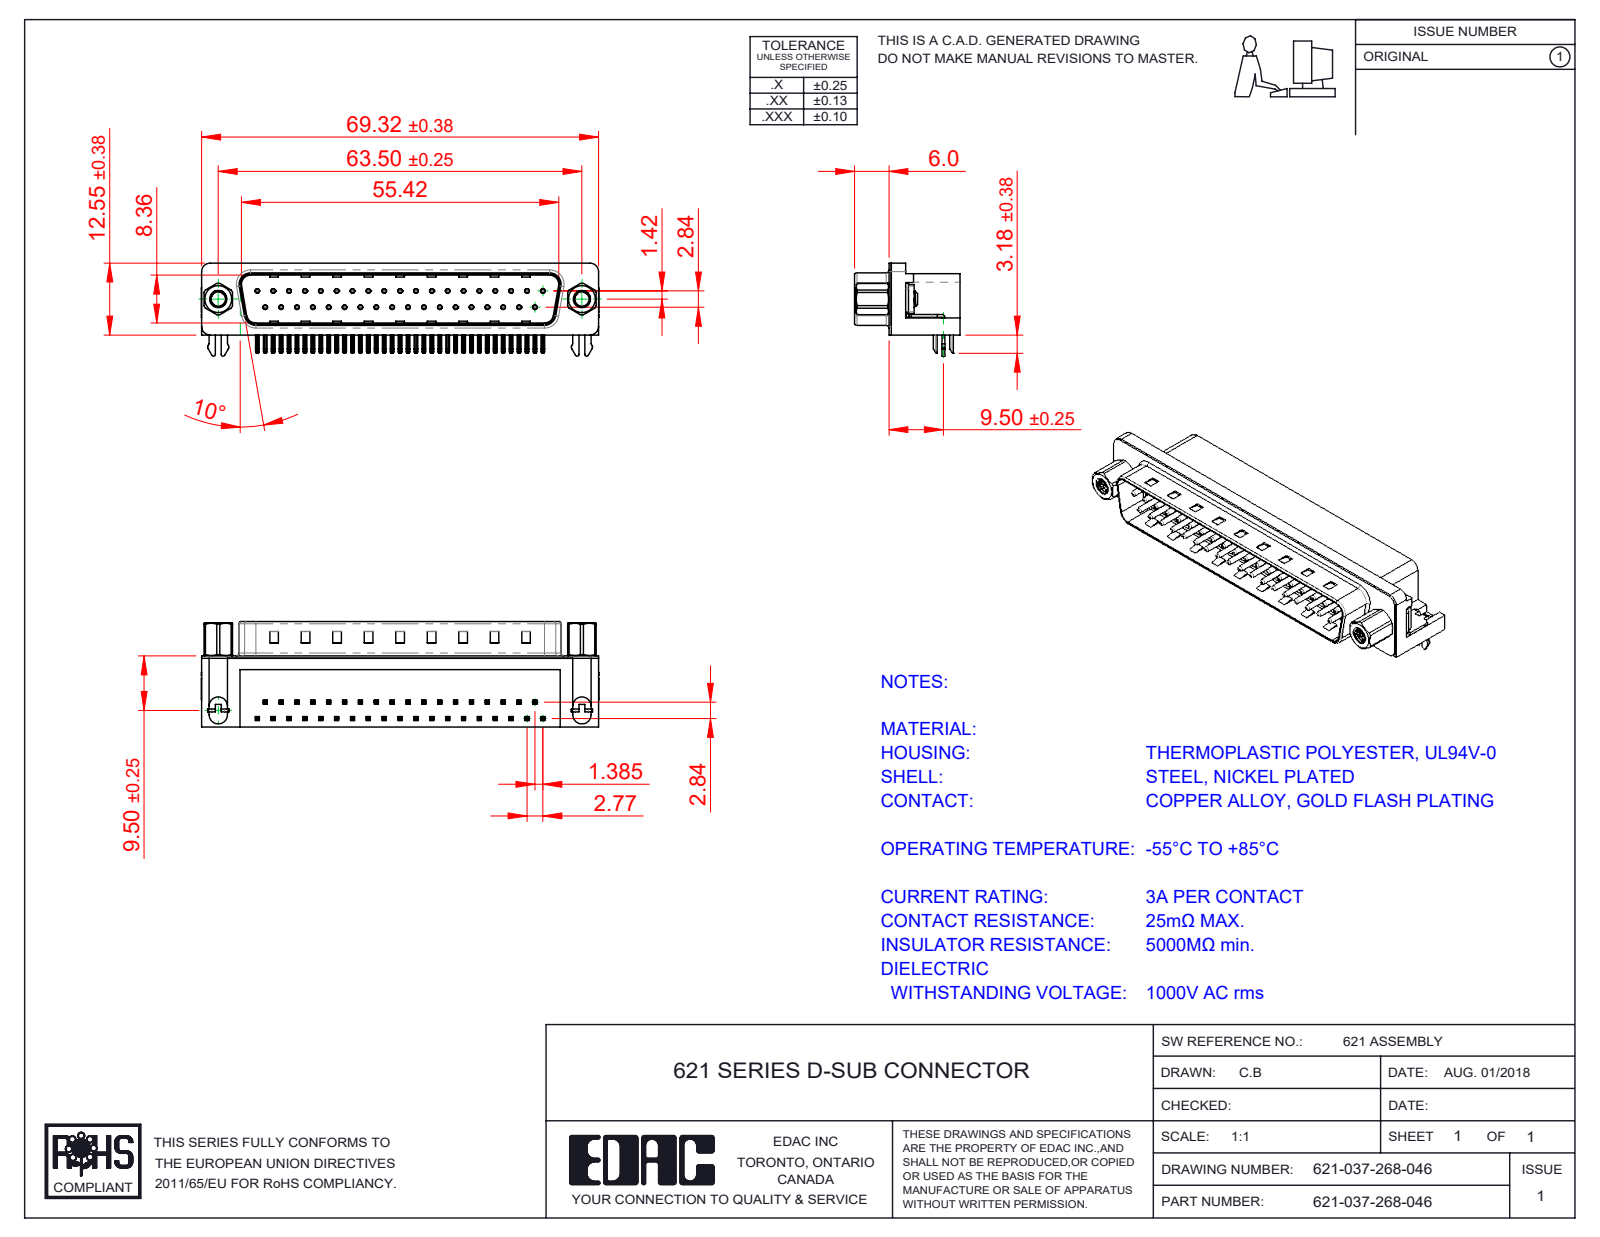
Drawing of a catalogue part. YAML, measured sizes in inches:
part_name: "621 4 Prong Board Lock; 621-037-268-046; 621 M3 Threaded Rivet; 621 M3 Hex Standoff 5 (+4 more)"
step_written_by: "SolidWorks 2016 (CONFIG_CONTROL_DESIGN)"
units: inches
bodies: {solids: 45, faces: 3467, planar: 2077, cylindrical: 1017, other: 373}
overall_size: [2.732, 0.724, 0.64]
volume: 0.541
surface_area: 16.59
round_holes:
  - {diameter: 0.014, count: 37}
  - {diameter: 0.031, count: 37}
  - {diameter: 0.079, count: 2}
  - {diameter: 0.098, count: 2}
  - {diameter: 0.157, count: 2}
  - {diameter: 0.189, count: 2}
  - {diameter: 0.197, count: 2}
round_bosses_or_shafts:
  - {diameter: 0.03, count: 37}
  - {diameter: 0.118, count: 4}
  - {diameter: 0.193, count: 2}
  - {diameter: 0.187, count: 2}
  - {diameter: 0.154, count: 2}
partial_cylinders:
  - {radius: 0.01, count: 160}
  - {radius: 0.005, count: 74}
  - {radius: 0.039, count: 16}
  - {radius: 0.02, count: 9}
  - {radius: 0.063, count: 8}
  - {radius: 0.059, count: 7}
  - {radius: 0.035, count: 4}
  - {radius: 0.079, count: 4}
face_to_face_distances: [0.016, 0.472, 0.407, 0.345, 0.083, 0.067, 0.412, 0.428, 0.354, 0.488]
hole_center_spacings: [0.124, 0.109, 0.218, 0.327, 0.436, 0.545, 0.763, 0.872]
